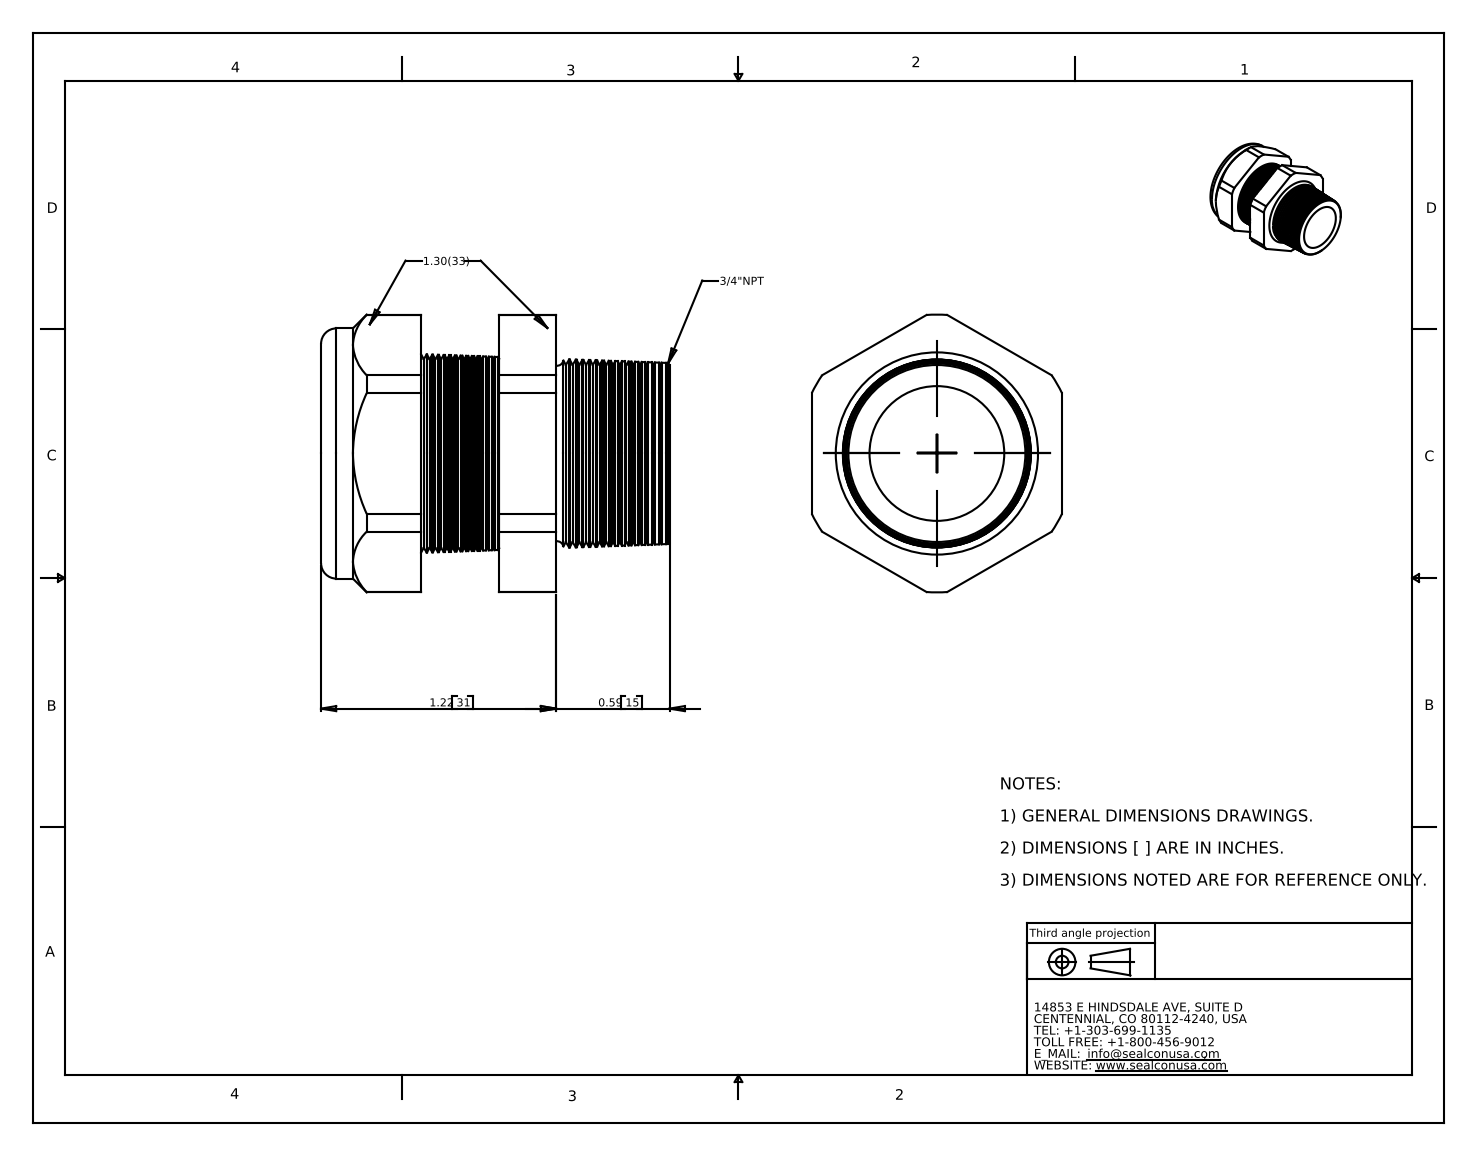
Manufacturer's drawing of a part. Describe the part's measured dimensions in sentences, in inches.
The part is named "CD21NP-BK". Its 3-D file was written by "SolidWorks 2007 (CONFIG_CONTROL_DESIGN)". It is 2 solids with 234 faces: 20 planar, 20 cylindrical and 194 other. Overall it measures 1.81 by 1.443 by 1.3 inches. Its volume is 1.304 cubic inches and its surface area 17.59 square inches. Round holes: 1 of diameter 0.69, 1 of diameter 0.71. Round bosses or shafts: 1 of diameter 1.3. Partial cylindrical surfaces (rounded edges, fillets, slot ends): 1 of radius 0.721. The main face-to-face distances are 1.3, 0.925, 0.52, 0.405, 1.22, 0.7, 0.295, 0.35, 0.17, 0.575.
